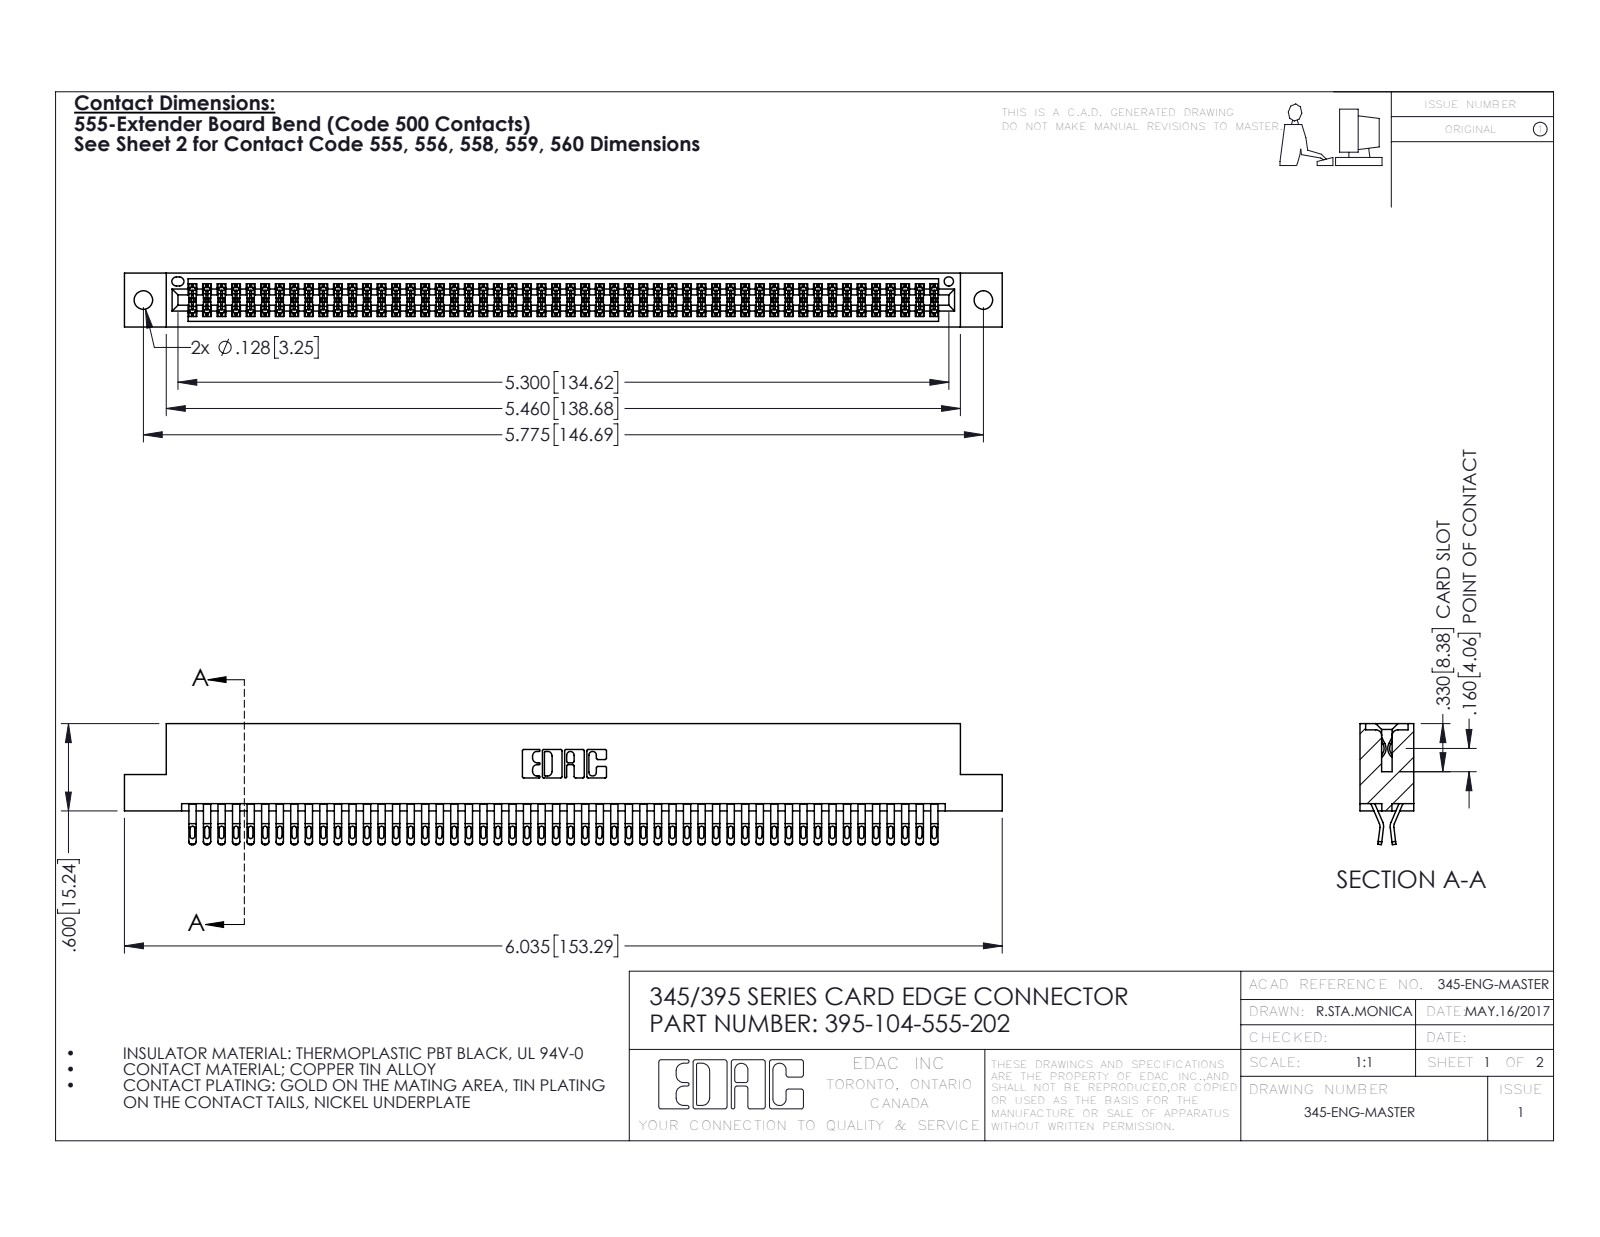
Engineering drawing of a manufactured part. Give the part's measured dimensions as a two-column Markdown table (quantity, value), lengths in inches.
| quantity | value |
| --- | --- |
| part name | 345 Part_Flush Mounting Lugs - 0.128 Dia; 345-292-001_555 Tail; 395-104-555-202 |
| STEP written by | SolidWorks 2016 (CONFIG_CONTROL_DESIGN) |
| units | inches |
| bodies | 105 solids, 5950 faces (3304 planar, 2646 cylindrical, 0 other) |
| overall size | 6.035 × 0.832 × 0.37 |
| volume | 0.931 in³ |
| surface area | 36.44 in² |
| round holes (diameter × count) | 0.128 × 2, 0.064 × 1 |
| partial cylindrical surfaces (radius × count) | 0.016 × 260, 0.02 × 208, 0.006 × 156, 0.01 × 22, 0.007 × 6, 0.031 × 6, 0.026 × 3, 0.01 × 2 |
| main face-to-face distances | 0.298, 0.072, 0.025, 0.37, 0.2, 0.098, 0.272, 0.225, 0.175, 0.149 |
| hole center spacings | 0.27, 5.539, 5.775 |
